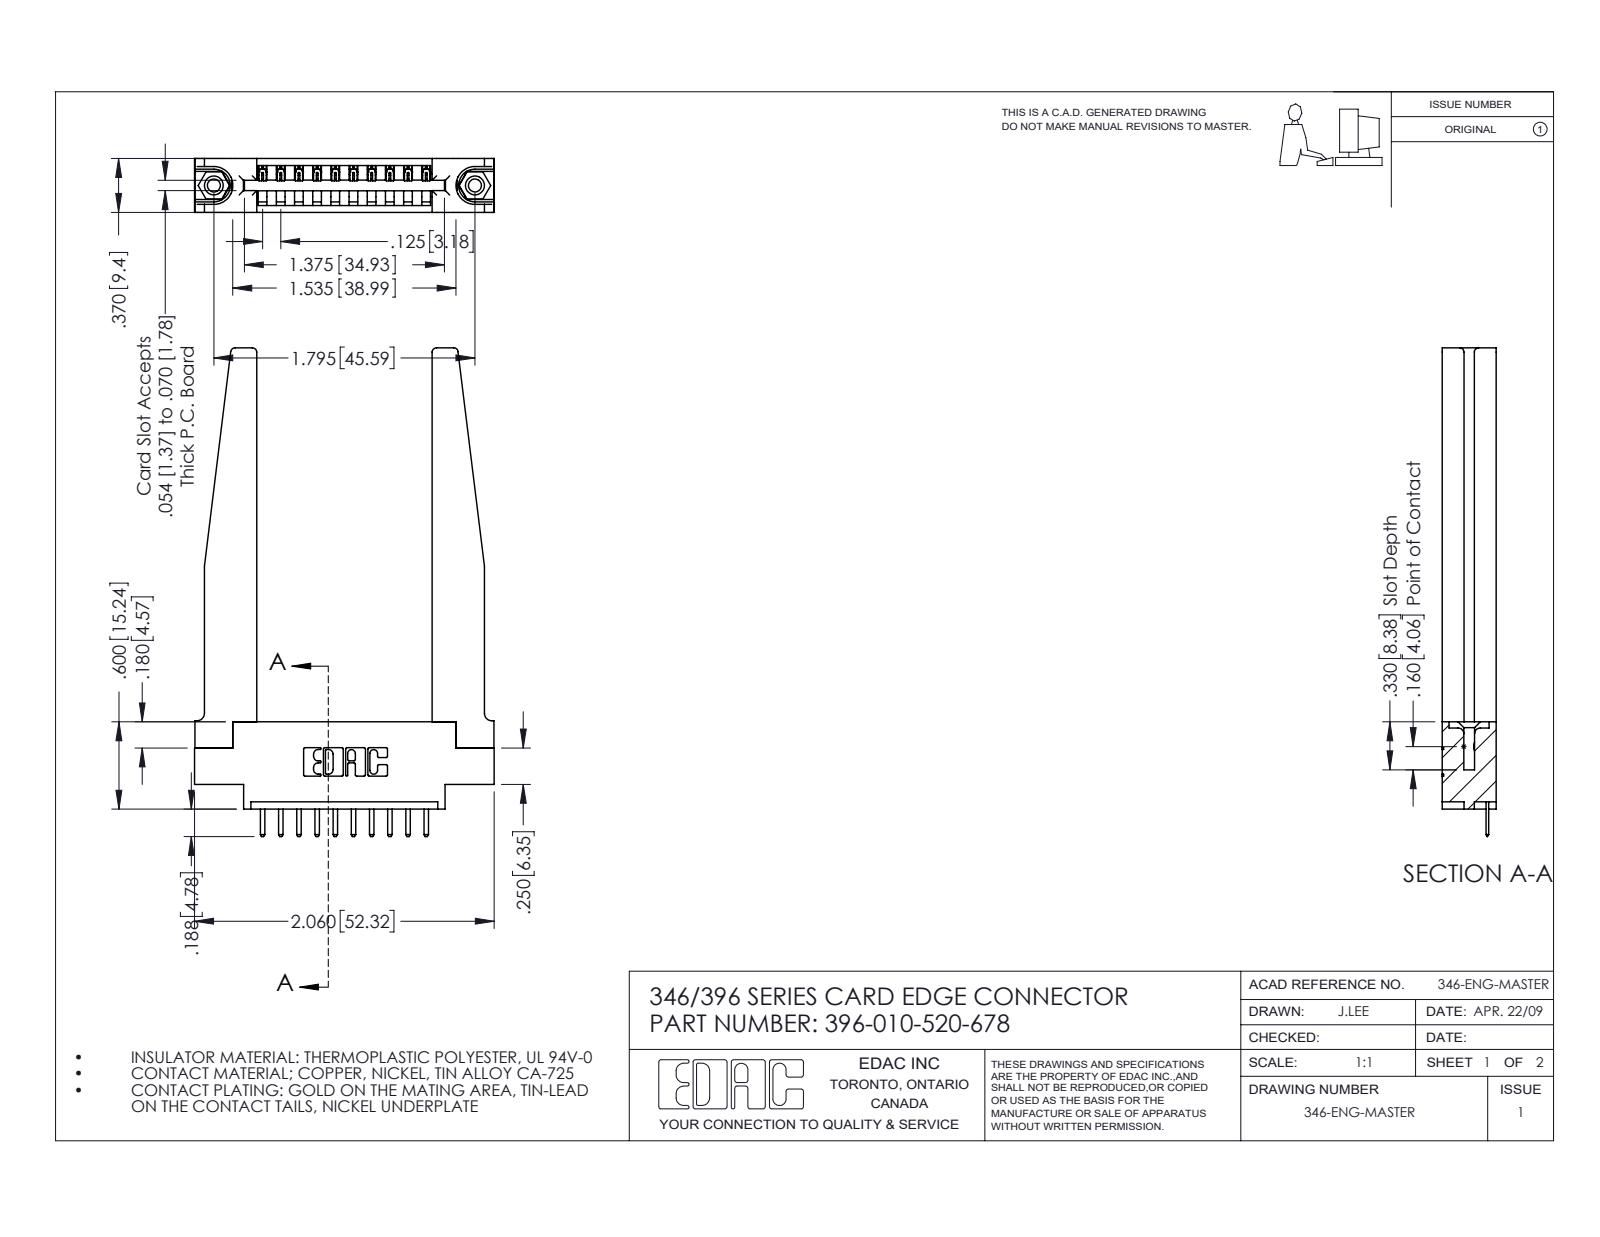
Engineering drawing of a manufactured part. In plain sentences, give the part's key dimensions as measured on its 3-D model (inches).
The part is named "345-250-001_345-250-001-102; 345-292-001_345-293-120; 396-010-520-678; 346-220-078_345-220-078 (+1 more)". Its 3-D file was written by "SolidWorks 2016 (CONFIG_CONTROL_DESIGN)". It is 15 solids with 980 faces: 642 planar, 286 cylindrical and 52 other. Overall it measures 3.358 by 2.06 by 0.37 inches. Its volume is 0.703 cubic inches and its surface area 18.62 square inches. Round holes: 2 of diameter 0.089, 2 of diameter 0.125, 2 of diameter 0.156, 1 of diameter 0.064. Round bosses or shafts: 2 of diameter 0.155. Partial cylindrical surfaces (rounded edges, fillets, slot ends): 22 of radius 0.01, 22 of radius 0.01, 20 of radius 0.006, 8 of radius 0.03, 6 of radius 0.007, 6 of radius 0.031, 3 of radius 0.026, 2 of radius 0.031. The main face-to-face distances are 0.37, 0.15, 0.072, 0.148, 0.22, 0.048, 0.322, 0.25, 0.102, 0.173. The hole center spacings are 0.246, 1.59, 1.795.
